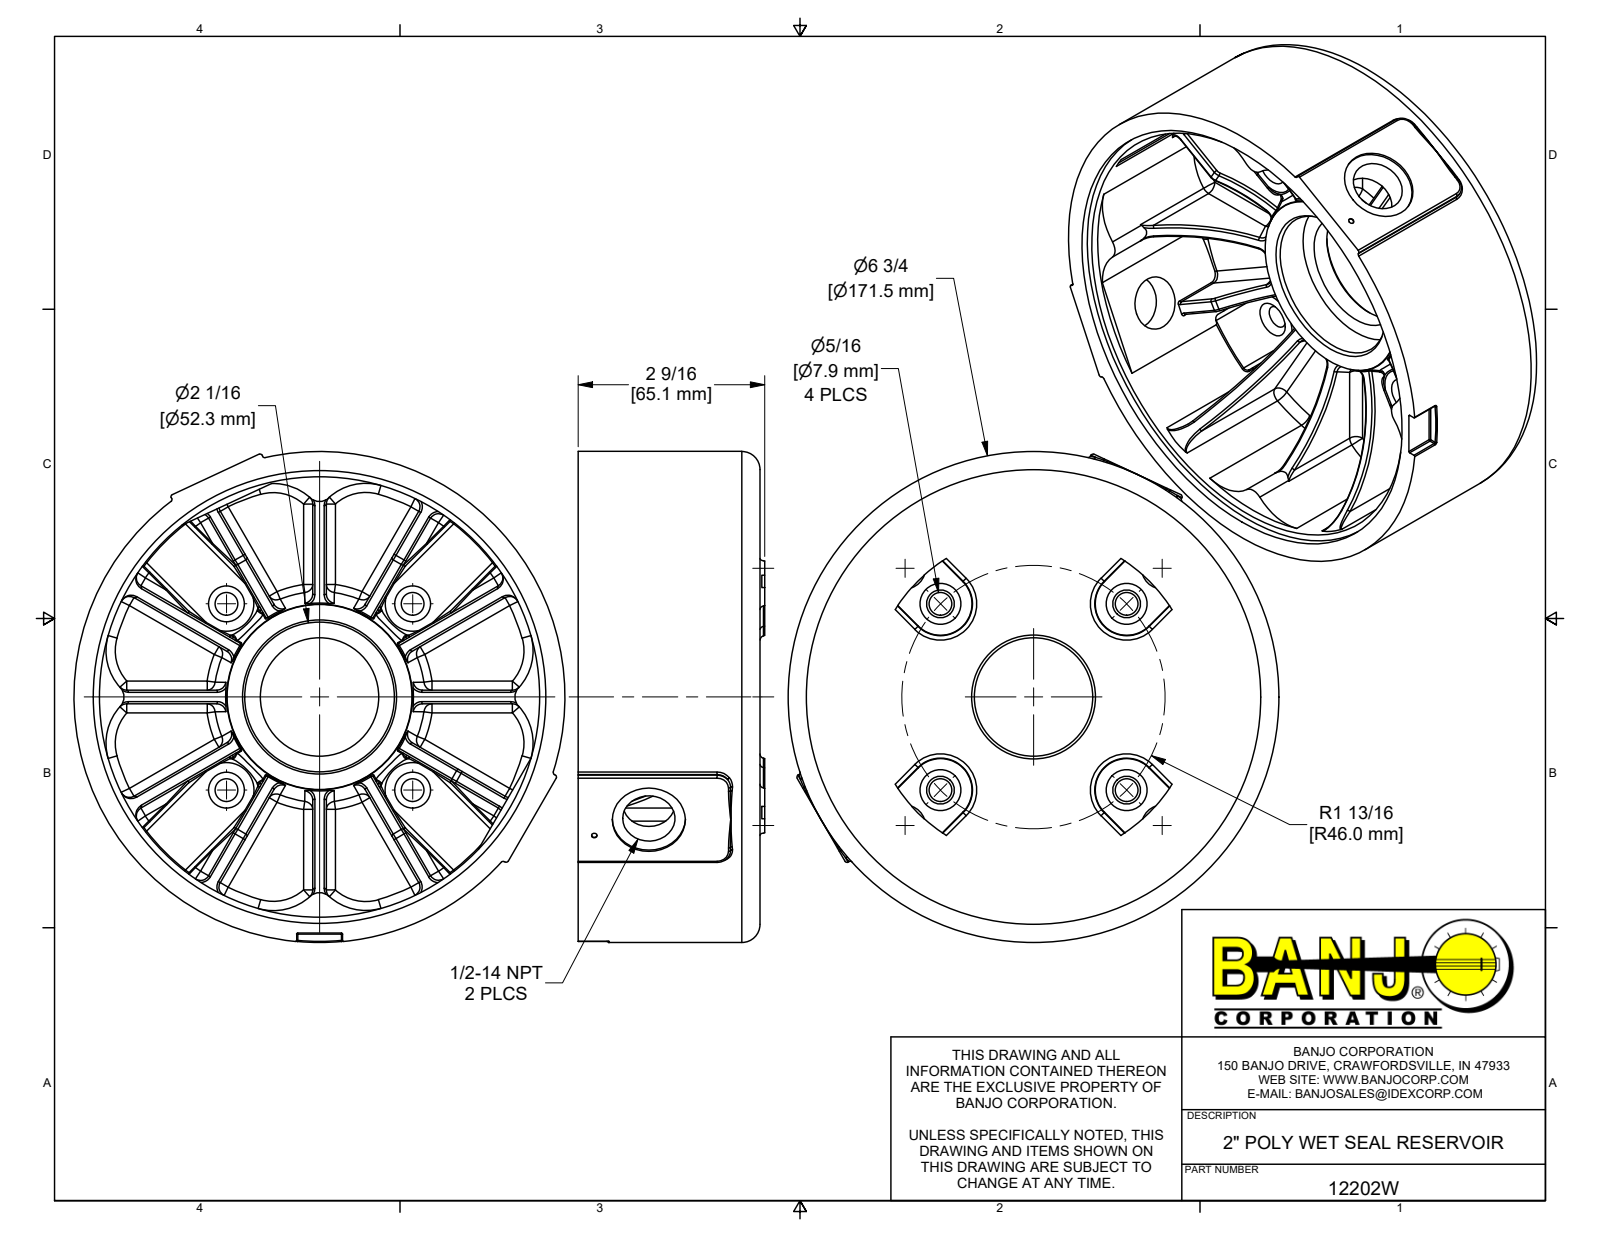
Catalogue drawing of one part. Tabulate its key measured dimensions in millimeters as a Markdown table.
| quantity | value |
| --- | --- |
| part name | 12202W; 12202WZ; 12202WY; 12202WX |
| STEP written by | Autodesk Inventor 2017 (AUTOMOTIVE_DESIGN) |
| units | millimeters |
| bodies | 1 solid, 637 faces (98 planar, 200 cylindrical, 339 other) |
| overall size | 171.45 × 171.45 × 65.1 |
| volume | 552 814 mm³ |
| surface area | 122 185 mm² |
| round holes (diameter × count) | 7.94 × 4, 14.25 × 4, 18.26 × 2, 25.53 × 2, 1.91 × 1, 41.4 × 1, 52.32 × 1, 153.67 × 1, 158.09 × 1 |
| round bosses / shafts (diameter × count) | 9.68 × 4, 171.45 × 1 |
| partial cylindrical surfaces (radius × count) | 3.17 × 41, 0.38 × 37, 1.52 × 24, 0.76 × 16, 63.5 × 12, 4.76 × 8, 19.05 × 8, 7.12 × 4 |
| main face-to-face distances | 4.76, 9.52, 63.48, 53.96, 11.11, 15.88, 6.36, 47.6, 19.79, 1.62 |
| hole center spacings | 45.98, 65.02, 91.95, 20.08 |
